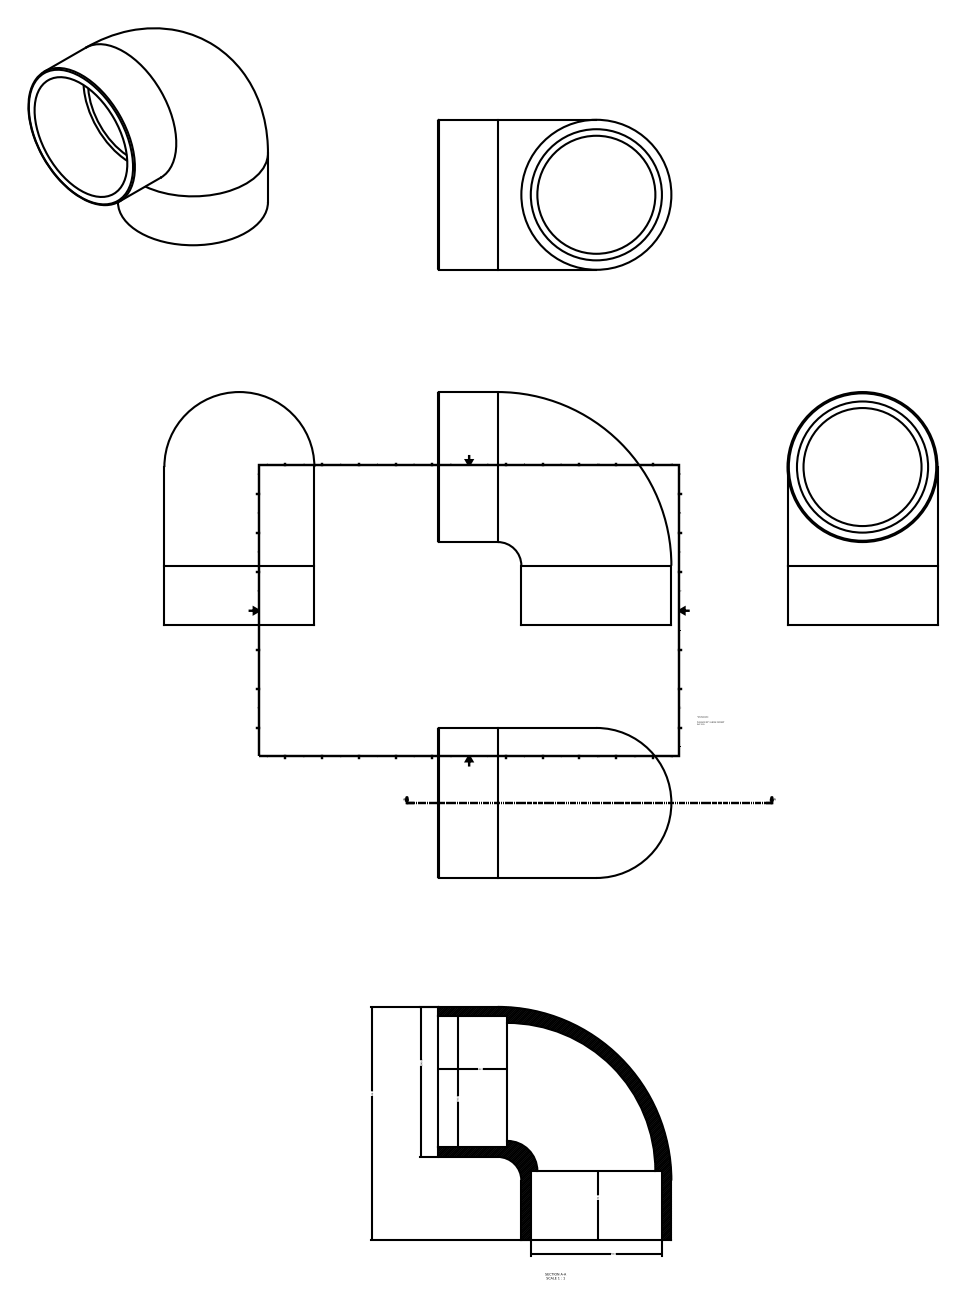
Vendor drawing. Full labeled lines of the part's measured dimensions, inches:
Part name (STEP PRODUCT): (_AS)050500250
STEP written by: Autodesk Inventor 2015 (AUTOMOTIVE_DESIGN)
Units: inches
Bodies: 1 solid, 11 faces (4 planar, 4 cylindrical, 3 other)
Overall size (bounding box): 17.52 × 17.52 × 11.26
Volume: 612.7 in³ · Surface area: 1 417 in²
Round holes (diameter × count): ⌀9.843 ×2
Round bosses / shafts (diameter × count): ⌀11.26 ×2
Main face-to-face distances: 5.197
